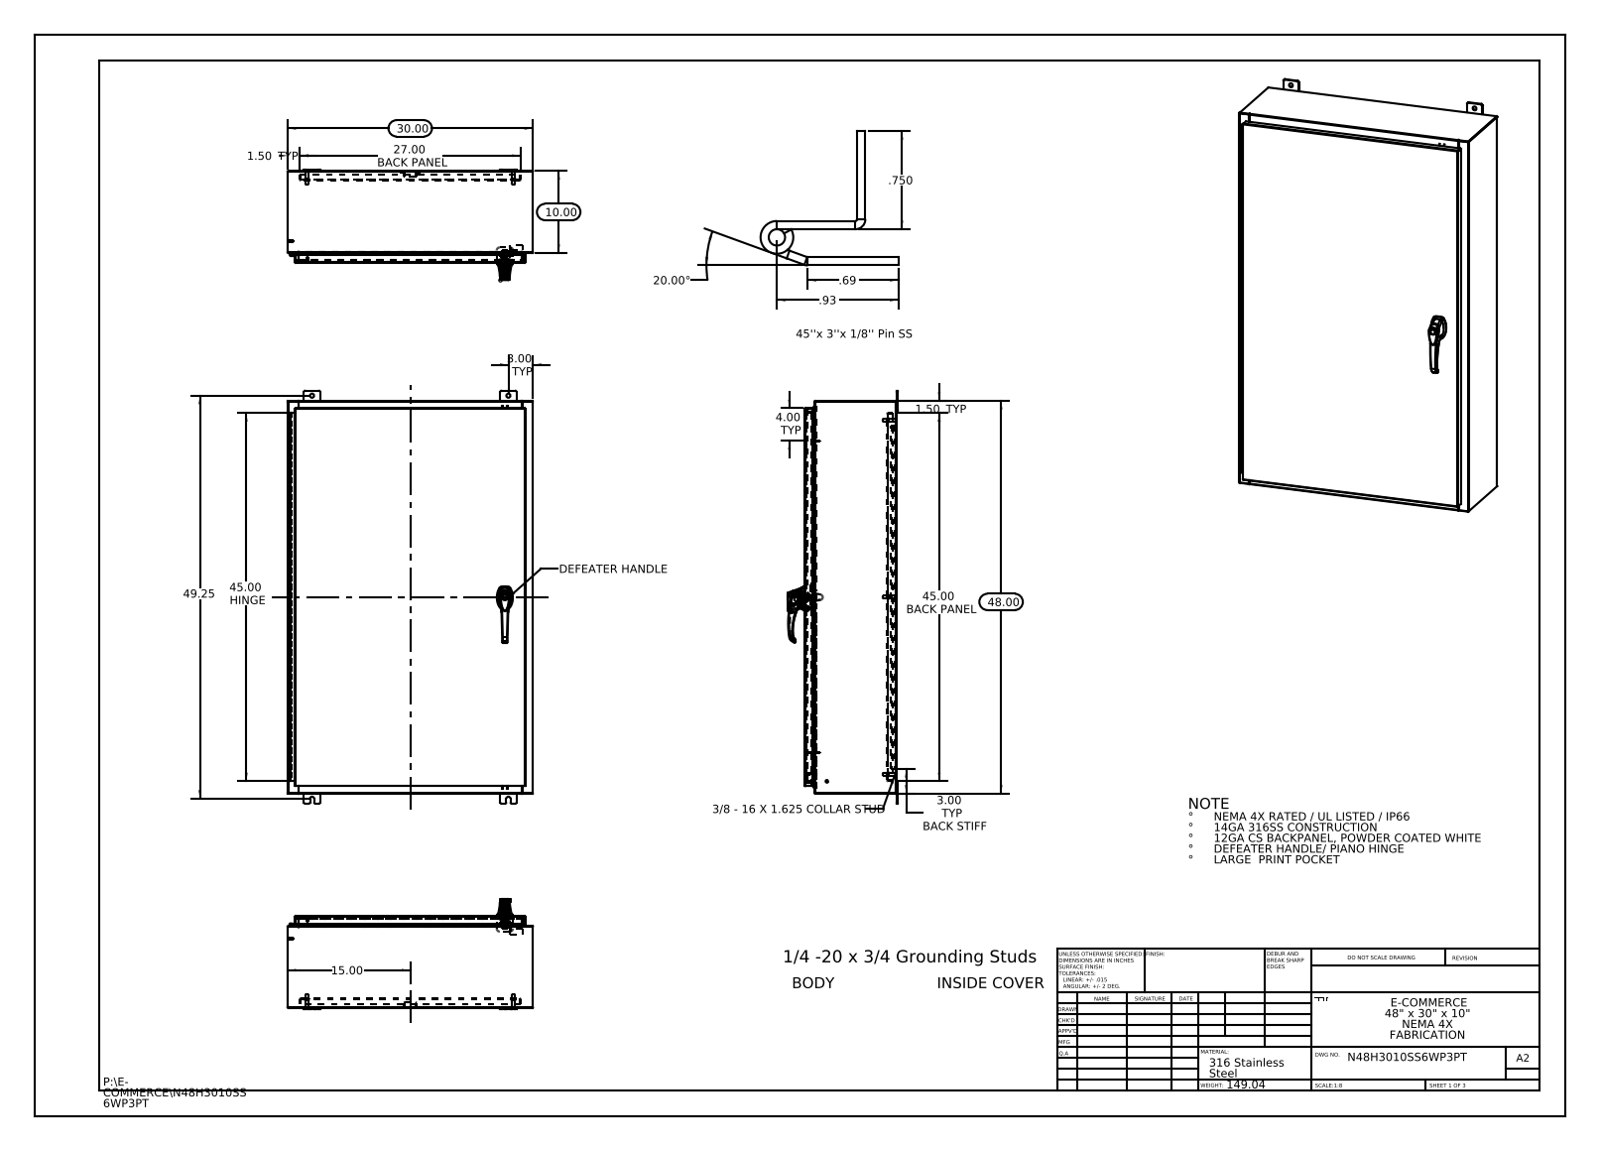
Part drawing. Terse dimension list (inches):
name: 21130102; Quarter-20 CD Stud; 10_30 CD Stud; N48H3010SS6WP3PT Cover (+8 more)
written by: SolidWorks 2013 (CONFIG_CONTROL_DESIGN)
unit: in
bodies: 40 solids, 3182 faces (1227 planar, 1237 cylindrical, 718 other)
size: 50.5 × 30 × 13.495
volume: 526.2 in³; area: 13 029 in²
holes: 10× ⌀0.5, 4× ⌀0.25, 3× ⌀0.138, 3× ⌀0.161, 2× ⌀0.079, 2× ⌀0.203, 2× ⌀0.313, 2× ⌀0.437, 1× ⌀0.125, 1× ⌀0.125, 1× ⌀0.197, 1× ⌀0.276
bosses: 6× ⌀0.625, 6× ⌀0.375, 6× ⌀0.33, 4× ⌀0.157, 4× ⌀0.14, 3× ⌀0.315, 3× ⌀0.236, 1× ⌀1.181
rounds: 37× R0.118, 33× R0.006, 28× R0.013, 24× R0.19, 22× R0.088, 15× R0.039, 12× R0.028, 6× R0.008
face distances: 0.075, 11.126, 11.051, 0.104, 11.201, 1, 10.126, 1.075, 10.051, 1.179
hole spacings: 17.357, 19.665, 21.625, 33.245, 25.25, 0.295, 0.625, 0.841
